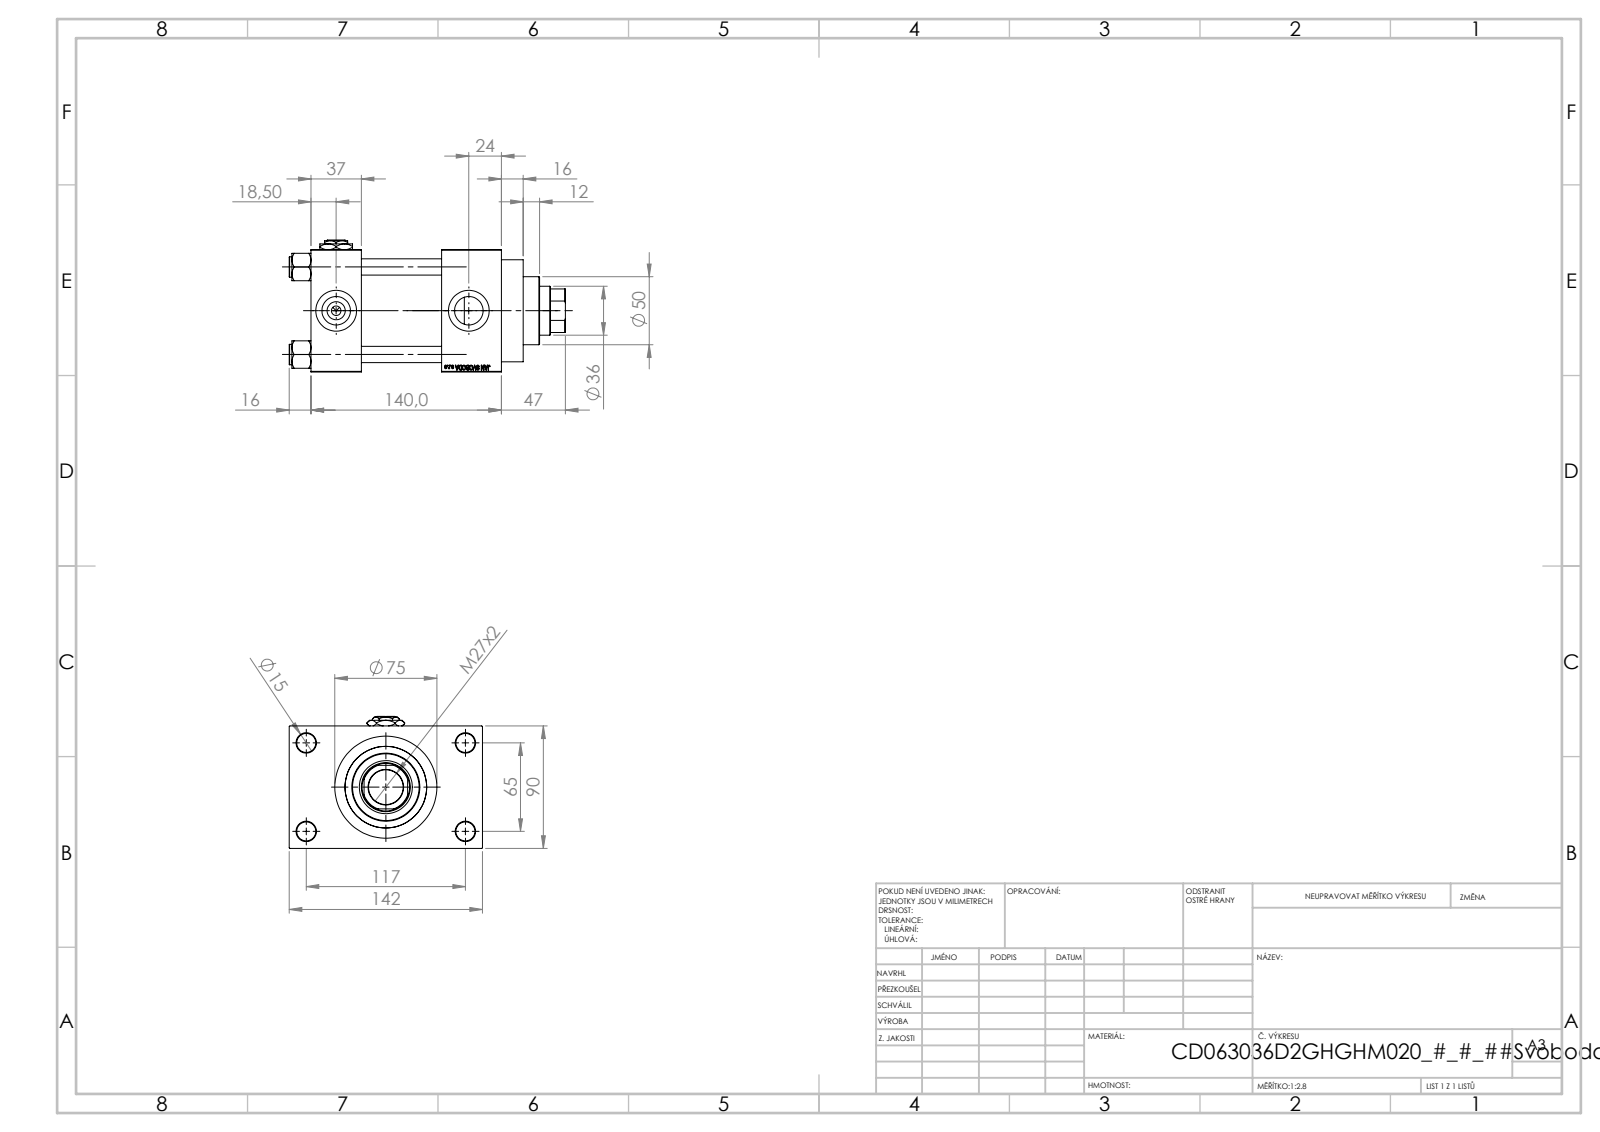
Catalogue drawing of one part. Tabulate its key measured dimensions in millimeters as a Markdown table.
| quantity | value |
| --- | --- |
| part name | V215CD_D_Body; Zatka_pro_OIL_PORT; V215CD_D_TYCINKA; V215CD_VC_A (+2 more) |
| STEP written by | SolidWorks 2019 (CONFIG_CONTROL_DESIGN) |
| units | millimeters |
| bodies | 12 solids, 1156 faces (521 planar, 95 cylindrical, 540 other) |
| overall size | 203 × 142 × 97 |
| volume | 1 109 000 mm³ |
| surface area | 208 556 mm² |
| round holes (diameter × count) | 12 × 4, 14 × 4, 7 × 3, 20.96 × 3, 30 × 3, 25.5 × 1, 36 × 1, 39 × 1, 50 × 1, 60 × 1, 63 × 1 |
| round bosses / shafts (diameter × count) | 15 × 4, 75 × 1, 69 × 1 |
| partial cylindrical surfaces (radius × count) | 17.5 × 1 |
| main face-to-face distances | 90, 59, 37, 96, 140, 103, 44, 26, 116, 142 |
| hole center spacings | 26.35, 45.47, 64.3, 66.92, 69.81, 90.65, 111.34, 65 |
